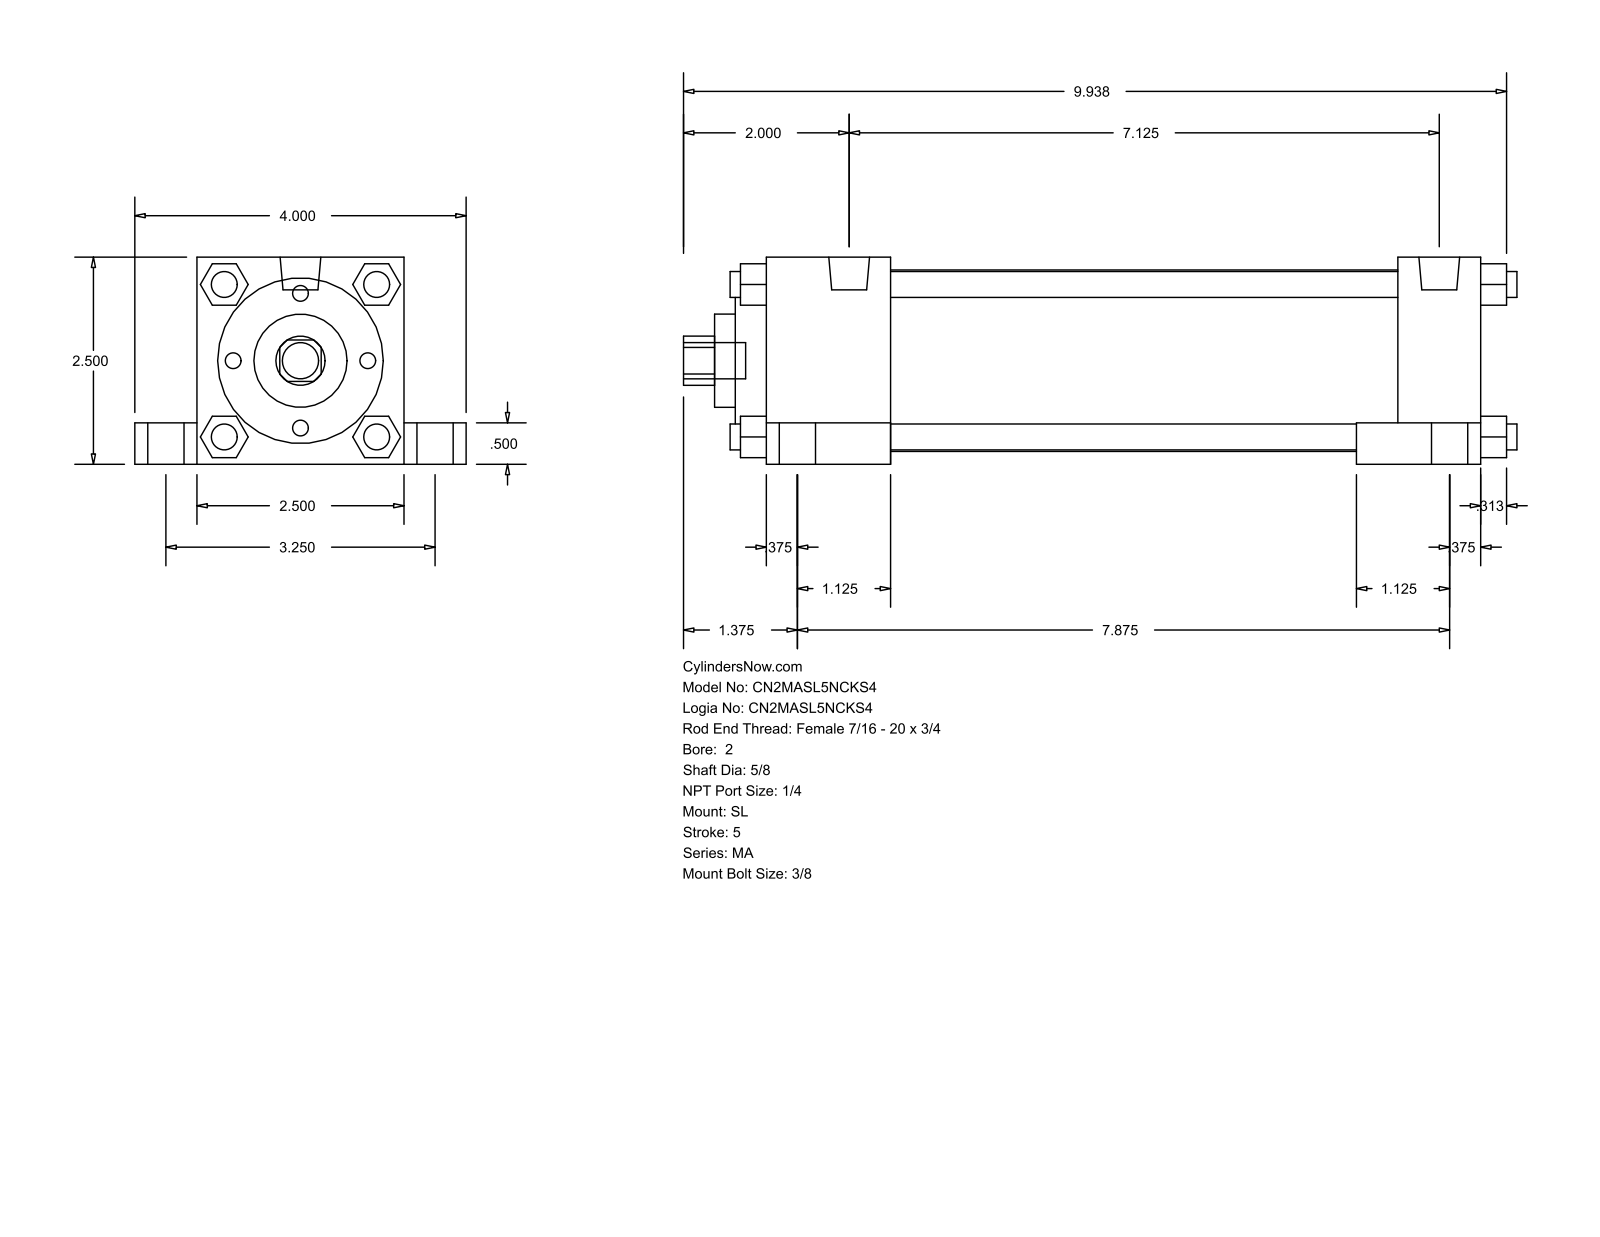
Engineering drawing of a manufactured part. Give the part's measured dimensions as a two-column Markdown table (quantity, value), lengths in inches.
| quantity | value |
| --- | --- |
| part name | MA_SL__0200_0.625 |
| STEP written by | GSSL Pune (CONFIG_CONTROL_DESIGN) |
| units | inches |
| bodies | 0 solids, 150 faces (113 planar, 37 cylindrical, 0 other) |
| overall size | 10.063 × 4 × 2.5 |
| round holes (diameter × count) | 0.625 × 1, 1.125 × 1, 2 × 1, 2.19 × 1 |
| round bosses / shafts (diameter × count) | 0.313 × 8, 0.437 × 5, 0.687 × 4, 0.492 × 2 |
| partial cylindrical surfaces (radius × count) | 0.297 × 1 |
| main face-to-face distances | 2.5, 0.5, 0.375, 6.125, 1, 0.75, 3.25, 1.5, 8.625, 2 |
